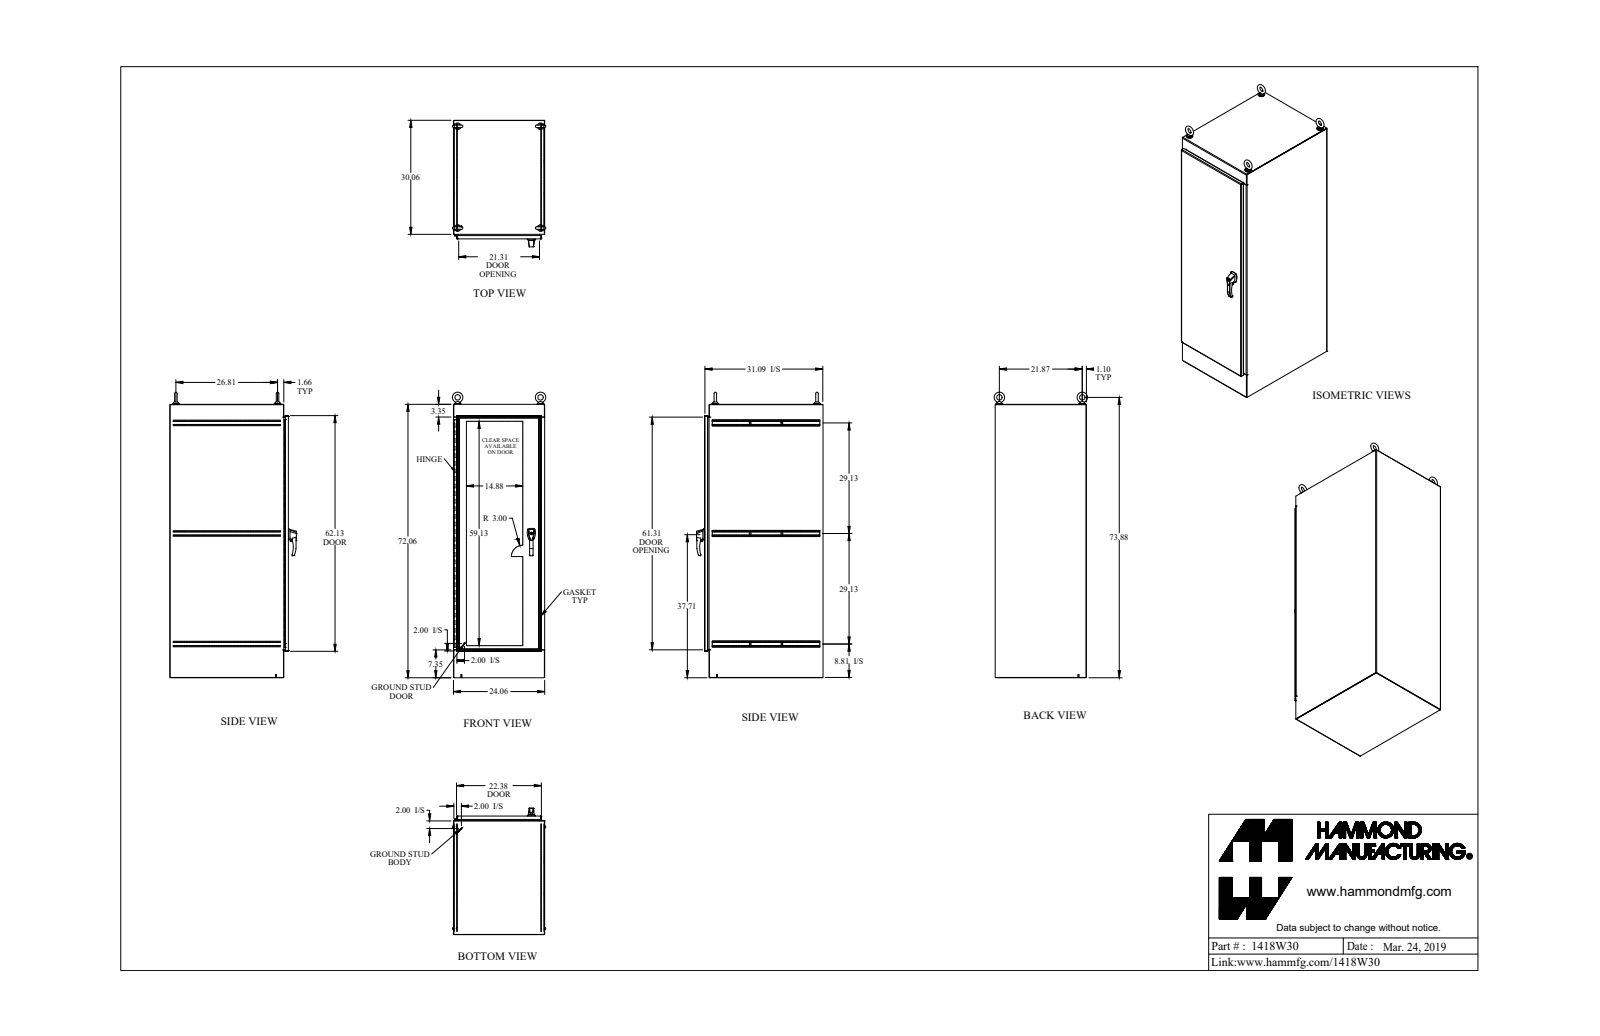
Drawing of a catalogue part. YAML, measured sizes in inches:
part_name: "1418W30_Default"
step_written_by: "SolidWorks 2019 (CONFIG_CONTROL_DESIGN)"
units: inches
bodies: {solids: 61, faces: 1880, planar: 813, cylindrical: 842, other: 225}
overall_size: [75.713, 33.362, 25.118]
volume: 1069
surface_area: 22355
round_holes:
  - {diameter: 0.304, count: 10}
  - {diameter: 0.5, count: 6}
  - {diameter: 0.527, count: 4}
  - {diameter: 0.625, count: 4}
  - {diameter: 0.687, count: 4}
  - {diameter: 0.75, count: 4}
  - {diameter: 0.25, count: 2}
  - {diameter: 0.257, count: 2}
  - {diameter: 0.28, count: 2}
  - {diameter: 0.281, count: 2}
  - {diameter: 0.313, count: 2}
  - {diameter: 0.39, count: 2}
round_bosses_or_shafts:
  - {diameter: 1.75, count: 4}
  - {diameter: 1.5, count: 4}
  - {diameter: 1.25, count: 4}
  - {diameter: 0.738, count: 4}
  - {diameter: 0.281, count: 4}
  - {diameter: 1, count: 2}
  - {diameter: 0.75, count: 2}
  - {diameter: 0.63, count: 2}
partial_cylinders:
  - {radius: 0.043, count: 42}
  - {radius: 0.138, count: 36}
  - {radius: 0.125, count: 22}
  - {radius: 0.018, count: 16}
  - {radius: 0.048, count: 13}
  - {radius: 0.143, count: 13}
  - {radius: 0.06, count: 10}
  - {radius: 0.015, count: 8}
face_to_face_distances: [0.095, 23.965, 31.152, 23.87, 24.06, 31.057, 71.965, 31.247, 1.187, 29.965]
hole_center_spacings: [6, 12, 18, 24, 30, 36, 8.375, 42]
